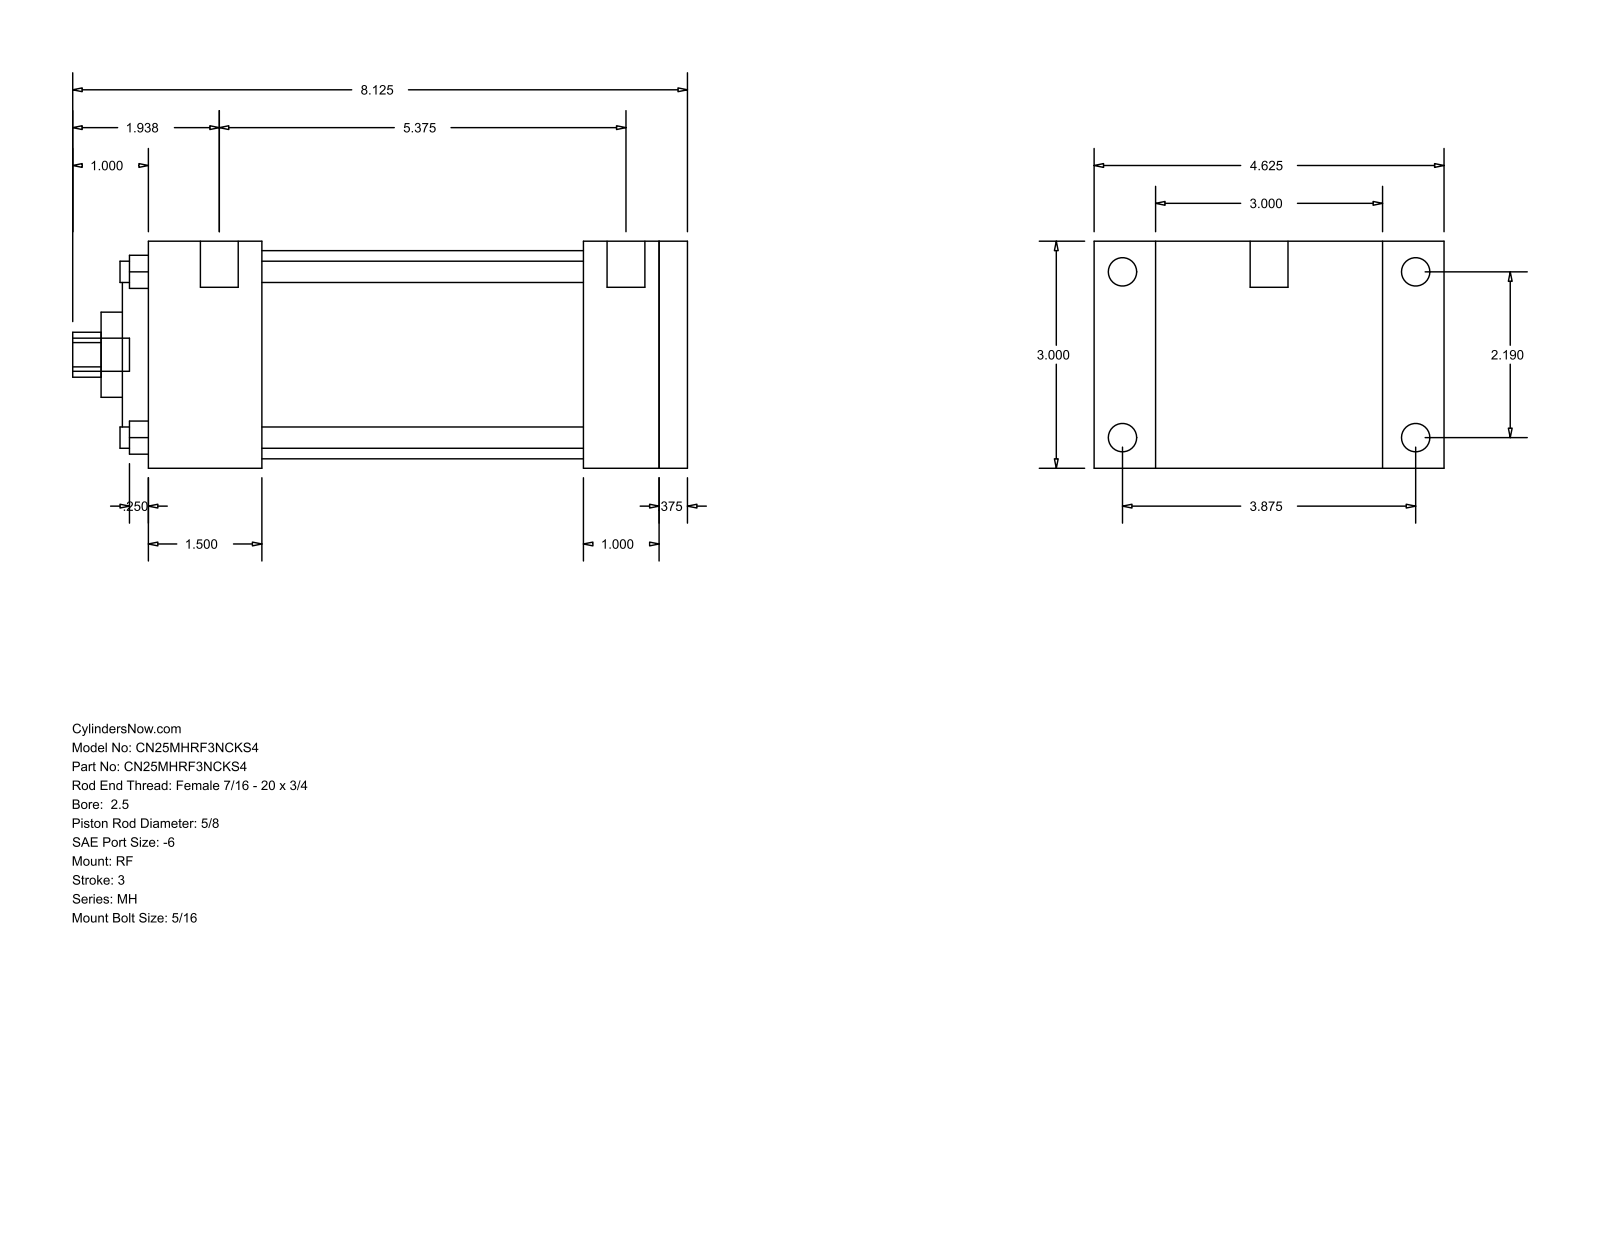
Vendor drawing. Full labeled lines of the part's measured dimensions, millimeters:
Part name (STEP PRODUCT): MH_RF__0250_0.625
STEP written by: GSSL Pune (CONFIG_CONTROL_DESIGN)
Units: millimetres
Bodies: 0 solids, 94 faces (65 planar, 29 cylindrical, 0 other)
Overall size (bounding box): 206.38 × 117.47 × 76.2
Round holes (diameter × count): ⌀7.14 ×4, ⌀15.88 ×1, ⌀28.57 ×1, ⌀55.55 ×1, ⌀69.85 ×1
Round bosses / shafts (diameter × count): ⌀9.53 ×4, ⌀5.56 ×4, ⌀12.7 ×2, ⌀11.11 ×1
Partial cylindrical surfaces — rounded edges, fillets, slot ends (radius × count): R7.54 ×1
Main face-to-face distances: 76.2, 9.53, 180.98, 171.45, 25.4, 146.05, 34.93, 38.1, 107.95, 133.35
Hole centre spacings: 39.33, 55.62, 78.66
